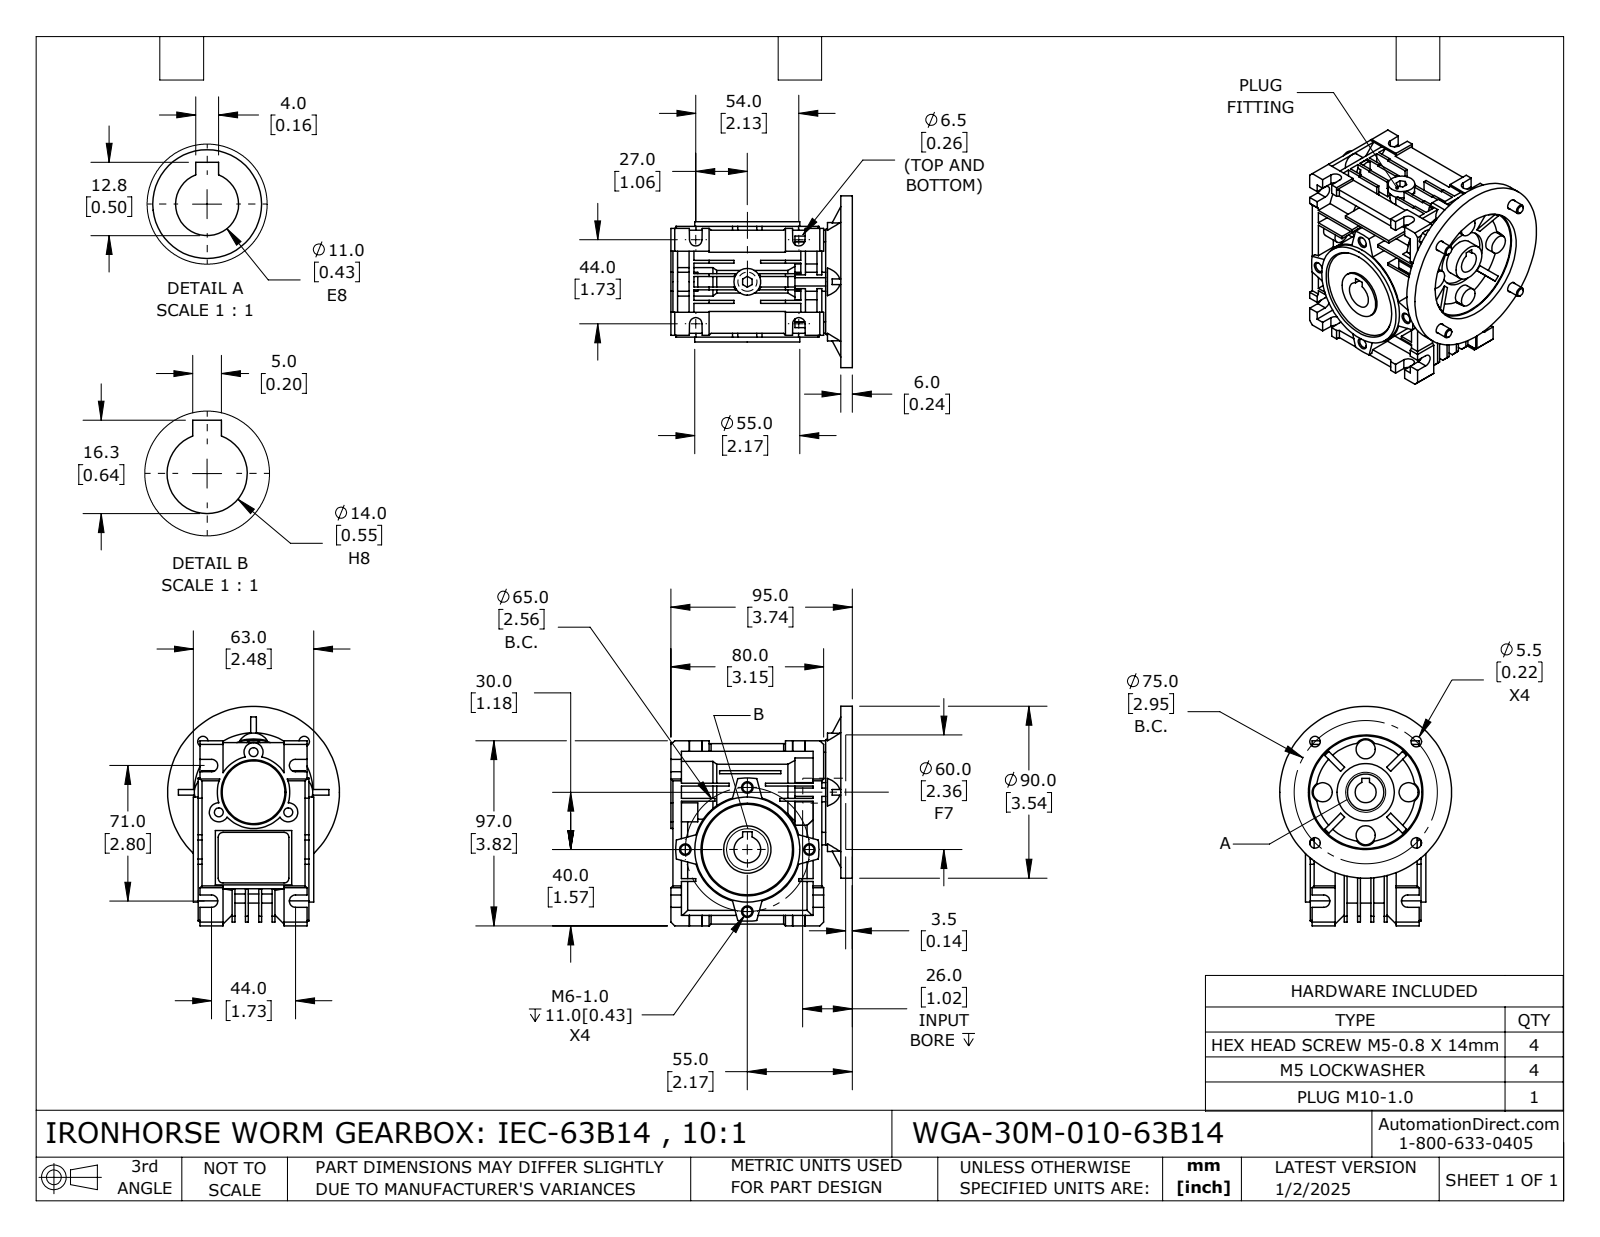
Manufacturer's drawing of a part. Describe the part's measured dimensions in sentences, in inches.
The part is named "WGA-30M-010-63B14". Its 3-D file was written by "SolidWorks 2024 (CONFIG_CONTROL_DESIGN)". It is 14 solids with 905 faces: 566 planar, 239 cylindrical and 100 other. Overall it measures 4.528 by 4.004 by 3.543 inches. Its volume is 20.73 cubic inches and its surface area 175.1 square inches. Round holes: 4 of diameter 0.194, 4 of diameter 0.201, 4 of diameter 0.217, 3 of diameter 0.183, 2 of diameter 0.194, 1 of diameter 0.354, 1 of diameter 0.433, 1 of diameter 0.453, 1 of diameter 0.551, 1 of diameter 0.571, 1 of diameter 0.748, 1 of diameter 0.976. Round bosses or shafts: 4 of diameter 0.394, 4 of diameter 0.362, 4 of diameter 0.197, 1 of diameter 3.543, 1 of diameter 2.205, 1 of diameter 2.165, 1 of diameter 1.496, 1 of diameter 1.457. Partial cylindrical surfaces (rounded edges, fillets, slot ends): 8 of radius 0.128, 4 of radius 0.098, 4 of radius 0.217, 4 of radius 0.335, 3 of radius 0.197, 1 of radius 0.295, 1 of radius 0.669, 1 of radius 0.846. The main face-to-face distances are 0.059, 0.276, 0.217, 0.039, 0.551, 0.177, 0.335, 0.236, 0.394, 0.079. The hole center spacings are 1.28, 1.476, 1.809, 2.088, 0.827, 0.711, 1.067, 1.432.
